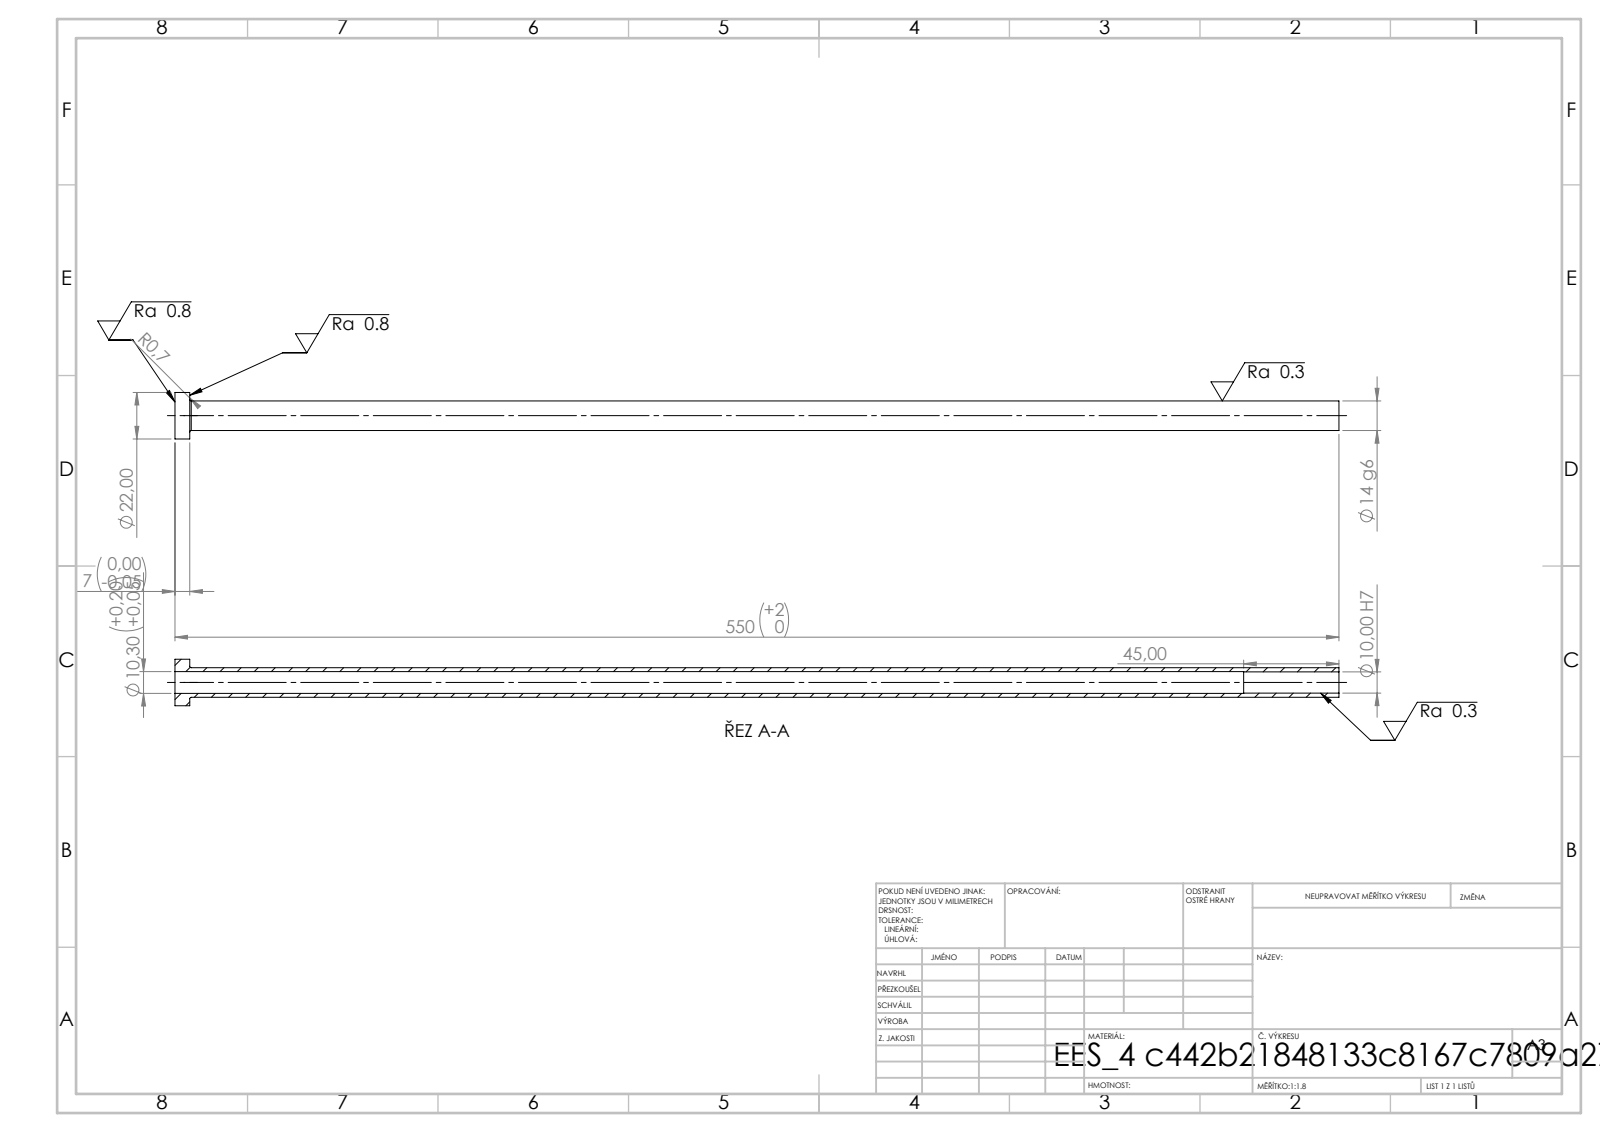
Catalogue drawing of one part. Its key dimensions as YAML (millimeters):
step_written_by: "SolidWorks 2019 (CONFIG_CONTROL_DESIGN)"
units: millimeters
bodies: {solids: 1, faces: 14, planar: 4, cylindrical: 8, other: 2}
overall_size: [550, 22, 22]
volume: 40642
surface_area: 42711
round_holes:
  - {diameter: 10, count: 1}
  - {diameter: 10.3, count: 1}
round_bosses_or_shafts:
  - {diameter: 22, count: 1}
  - {diameter: 14, count: 1}
face_to_face_distances: [7, 550, 543, 505, 498, 45]
